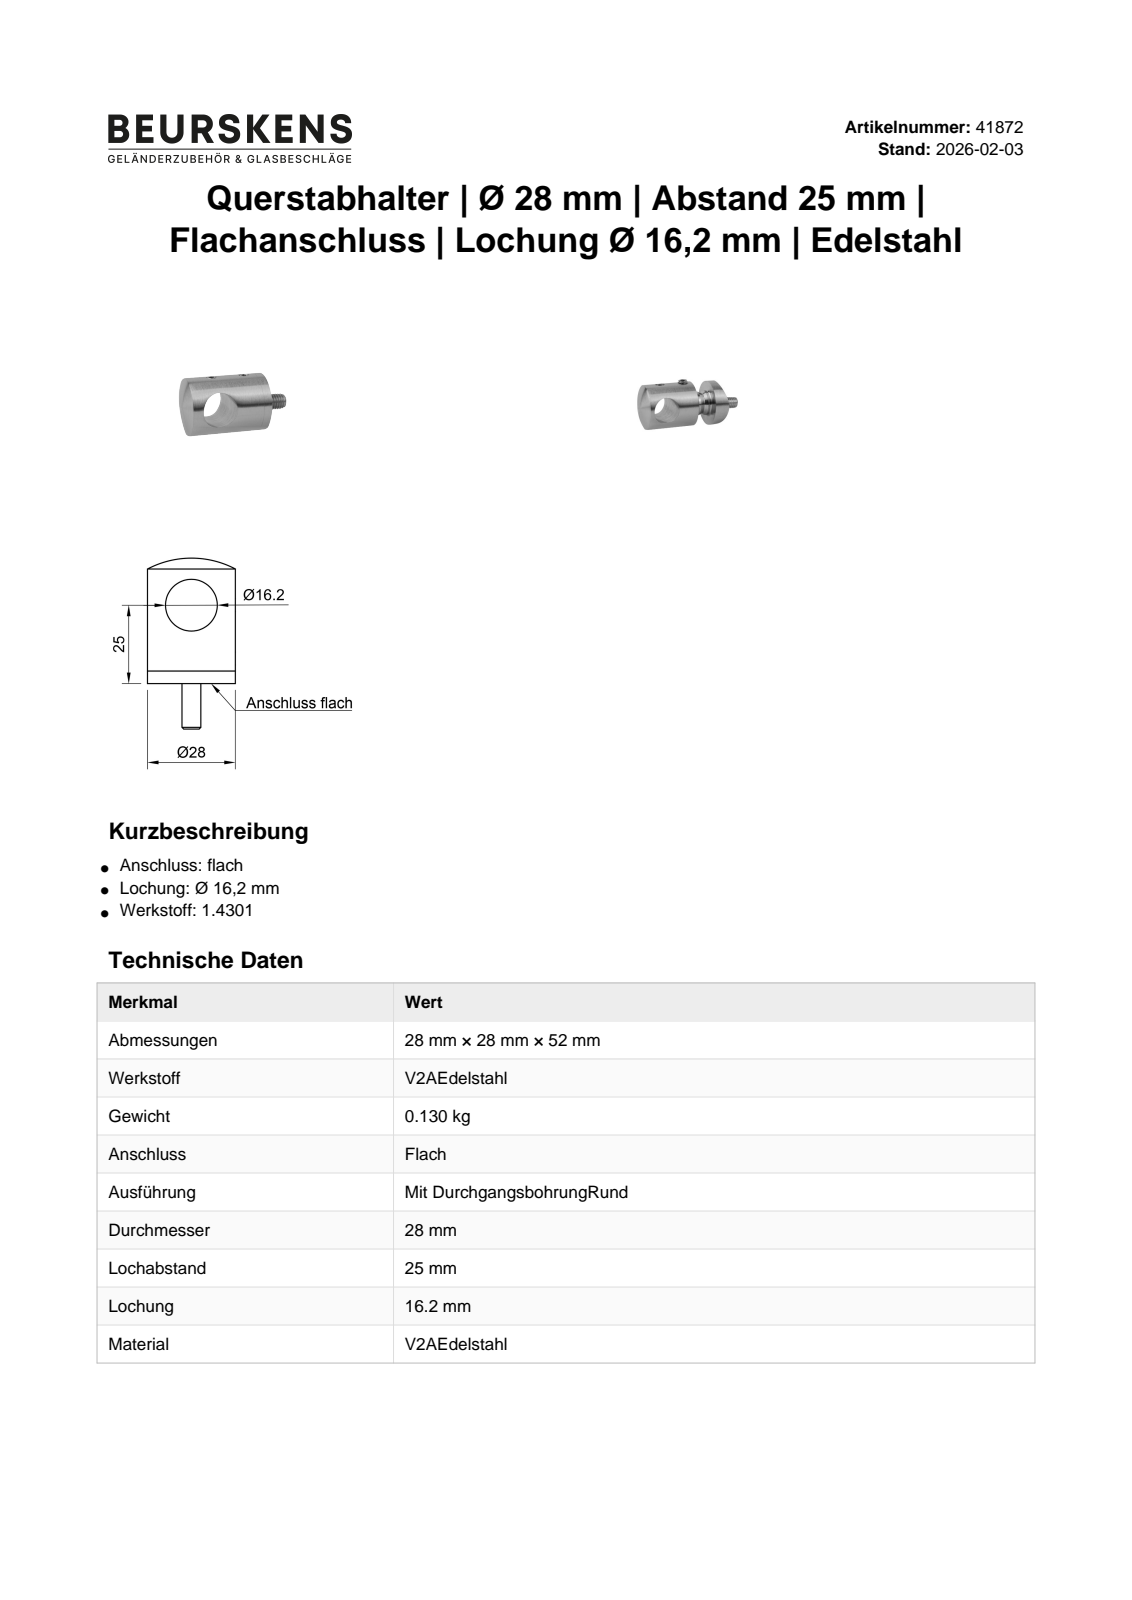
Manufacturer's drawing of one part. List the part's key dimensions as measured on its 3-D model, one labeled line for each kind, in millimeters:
Part name (STEP PRODUCT): H-22-42.4ñ; socket countersunk head screw_din_DIN 7991 - M6 x 25 --- 18.7N; socket set screw flat point_din_DIN 913 - M5 x 5-N; 41872 for customer
STEP written by: SolidWorks 2020 (CONFIG_CONTROL_DESIGN)
Units: millimetres
Bodies: 5 solids, 96 faces (38 planar, 26 cylindrical, 32 other)
Overall size (bounding box): 54.48 × 28 × 28
Volume: 17 785 mm³ · Surface area: 8 337 mm²
Round holes (diameter × count): ⌀4 ×2, ⌀7 ×1, ⌀11.2 ×1, ⌀14 ×1, ⌀16.5 ×1
Round bosses / shafts (diameter × count): ⌀5 ×2, ⌀28 ×1, ⌀12.8 ×1, ⌀11.57 ×1, ⌀6 ×1
Main face-to-face distances: 4, 2, 10.51, 6.51, 8.51, 13.5, 11.5, 9.5, 2.99, 6
Hole centre spacings: 17
